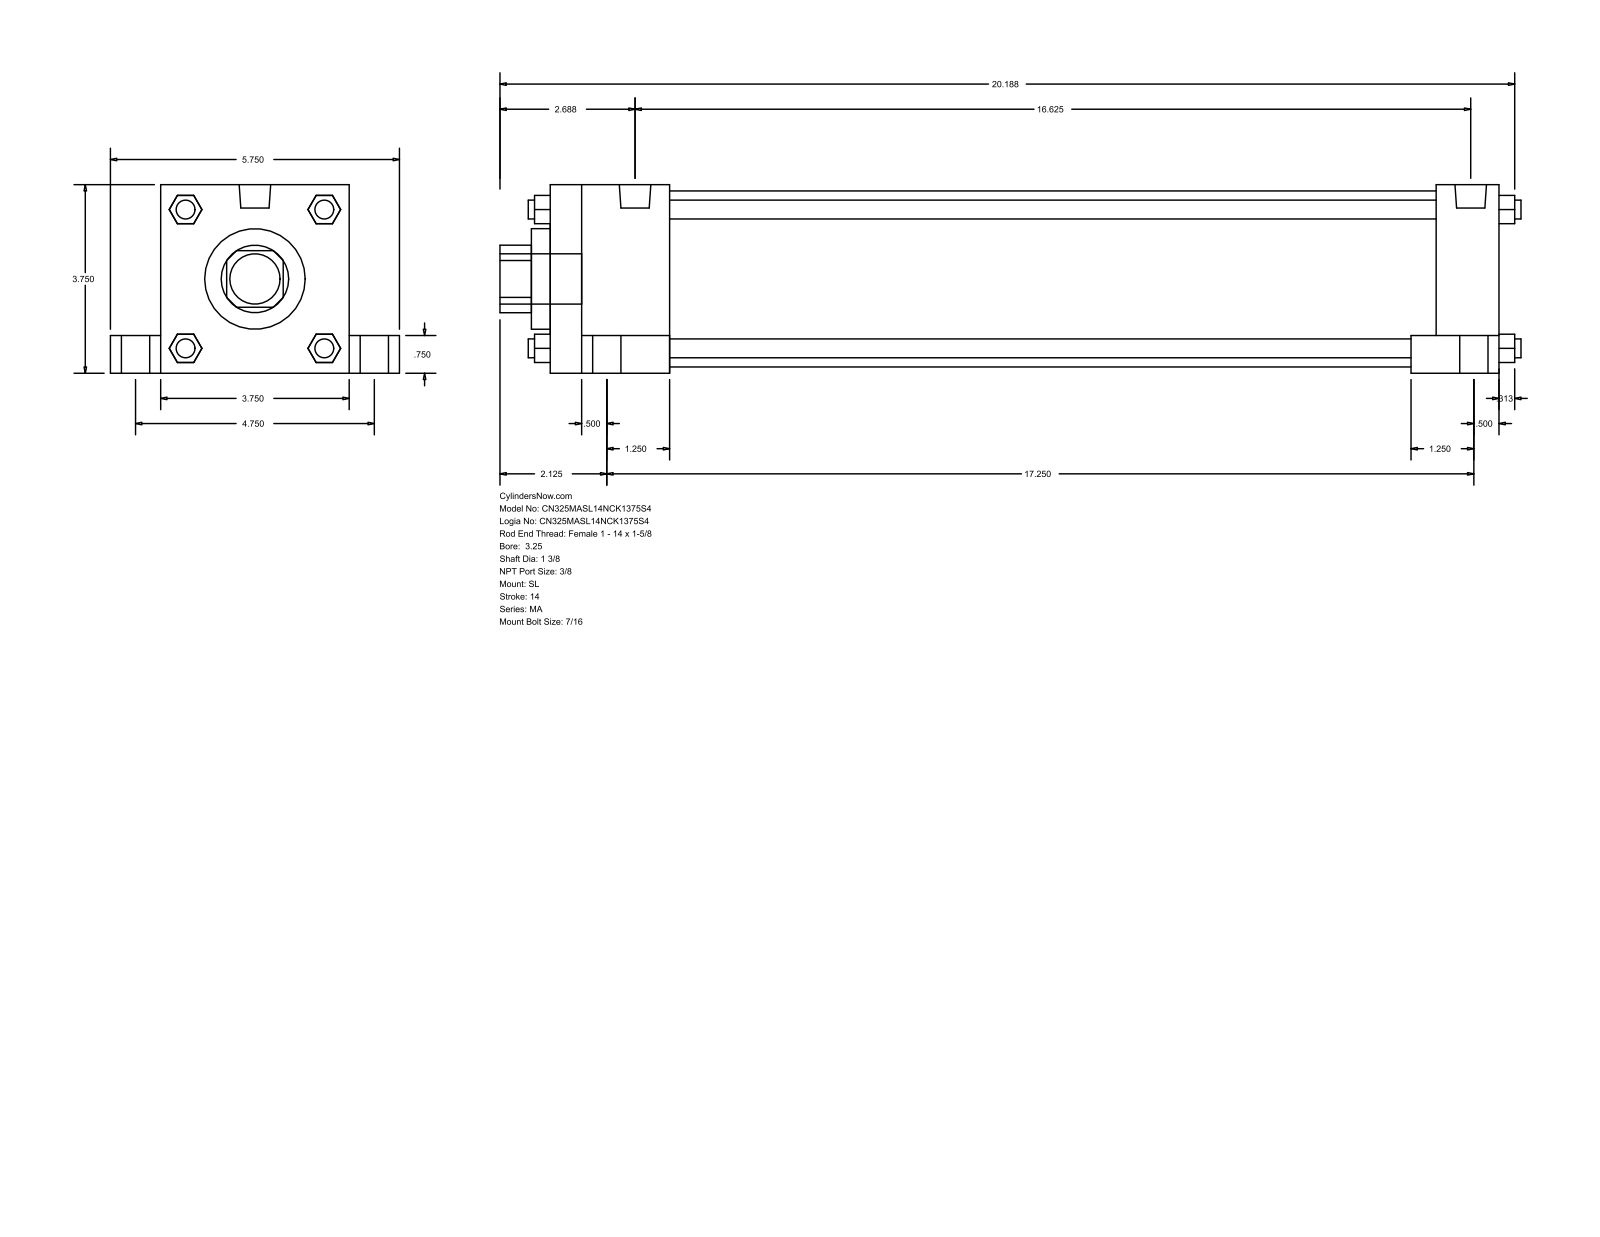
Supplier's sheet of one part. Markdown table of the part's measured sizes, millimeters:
| quantity | value |
| --- | --- |
| part name | MA_SL__0325_1.375 |
| STEP written by | GSSL Pune (CONFIG_CONTROL_DESIGN) |
| units | millimeters |
| bodies | 0 solids, 148 faces (112 planar, 36 cylindrical, 0 other) |
| overall size | 515.94 × 146.05 × 95.25 |
| round holes (diameter × count) | 34.92 × 1, 50.8 × 1, 88.9 × 1 |
| round bosses / shafts (diameter × count) | 20.64 × 4, 14.29 × 4, 11.11 × 4, 9.53 × 4, 15.93 × 2, 25.4 × 1 |
| partial cylindrical surfaces (radius × count) | 17.06 × 1 |
| main face-to-face distances | 95.24, 479.42, 387.35, 25.41, 120.65, 447.67, 31.75, 60.32, 419.1, 19.05 |
